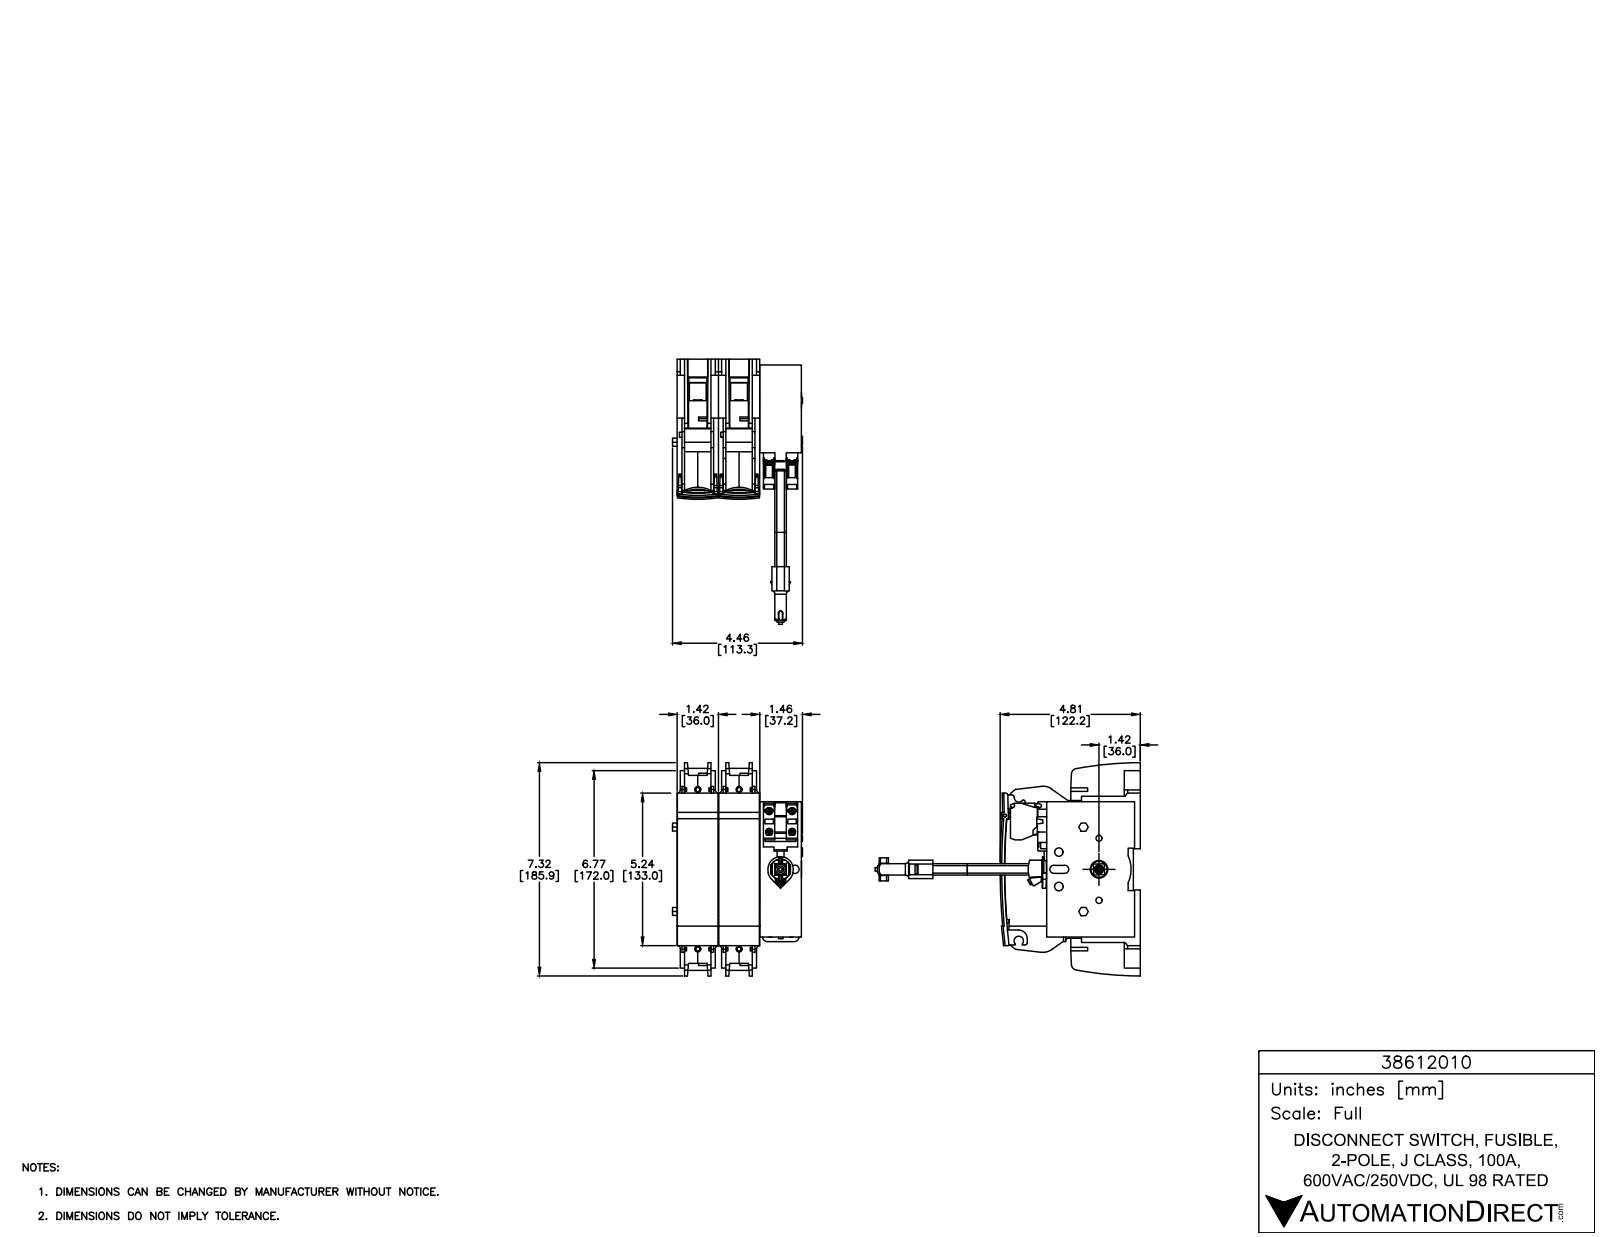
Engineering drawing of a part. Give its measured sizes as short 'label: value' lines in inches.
name: 38612010
written by: SolidWorks 2015 (AUTOMOTIVE_DESIGN)
unit: in
bodies: 5 solids, 1307 faces (762 planar, 234 cylindrical, 311 other)
size: 7.323 × 4.813 × 4.303
volume: 90.07 in³; area: 306.7 in²
holes: 4× ⌀0.205, 2× ⌀0.209, 2× ⌀0.211, 2× ⌀0.295, 1× ⌀0.098, 1× ⌀0.102, 1× ⌀0.13, 1× ⌀0.283, 1× ⌀0.602, 1× ⌀0.622
bosses: 2× ⌀0.287, 2× ⌀0.205, 2× ⌀0.203, 1× ⌀0.63, 1× ⌀0.315, 1× ⌀0.197
rounds: 16× R0.106, 8× R0.248, 8× R0.346, 5× R0.02, 5× R0.039, 4× R0.043, 4× R0.201, 3× R0.138
face distances: 1.417, 0.256, 1.161, 2.835, 0.165, 1.252, 0.091, 0.996, 1.421, 2.839
hole spacings: 1.067, 1.417, 1.458, 1.499, 2.156, 3.339, 4.311, 5.472
